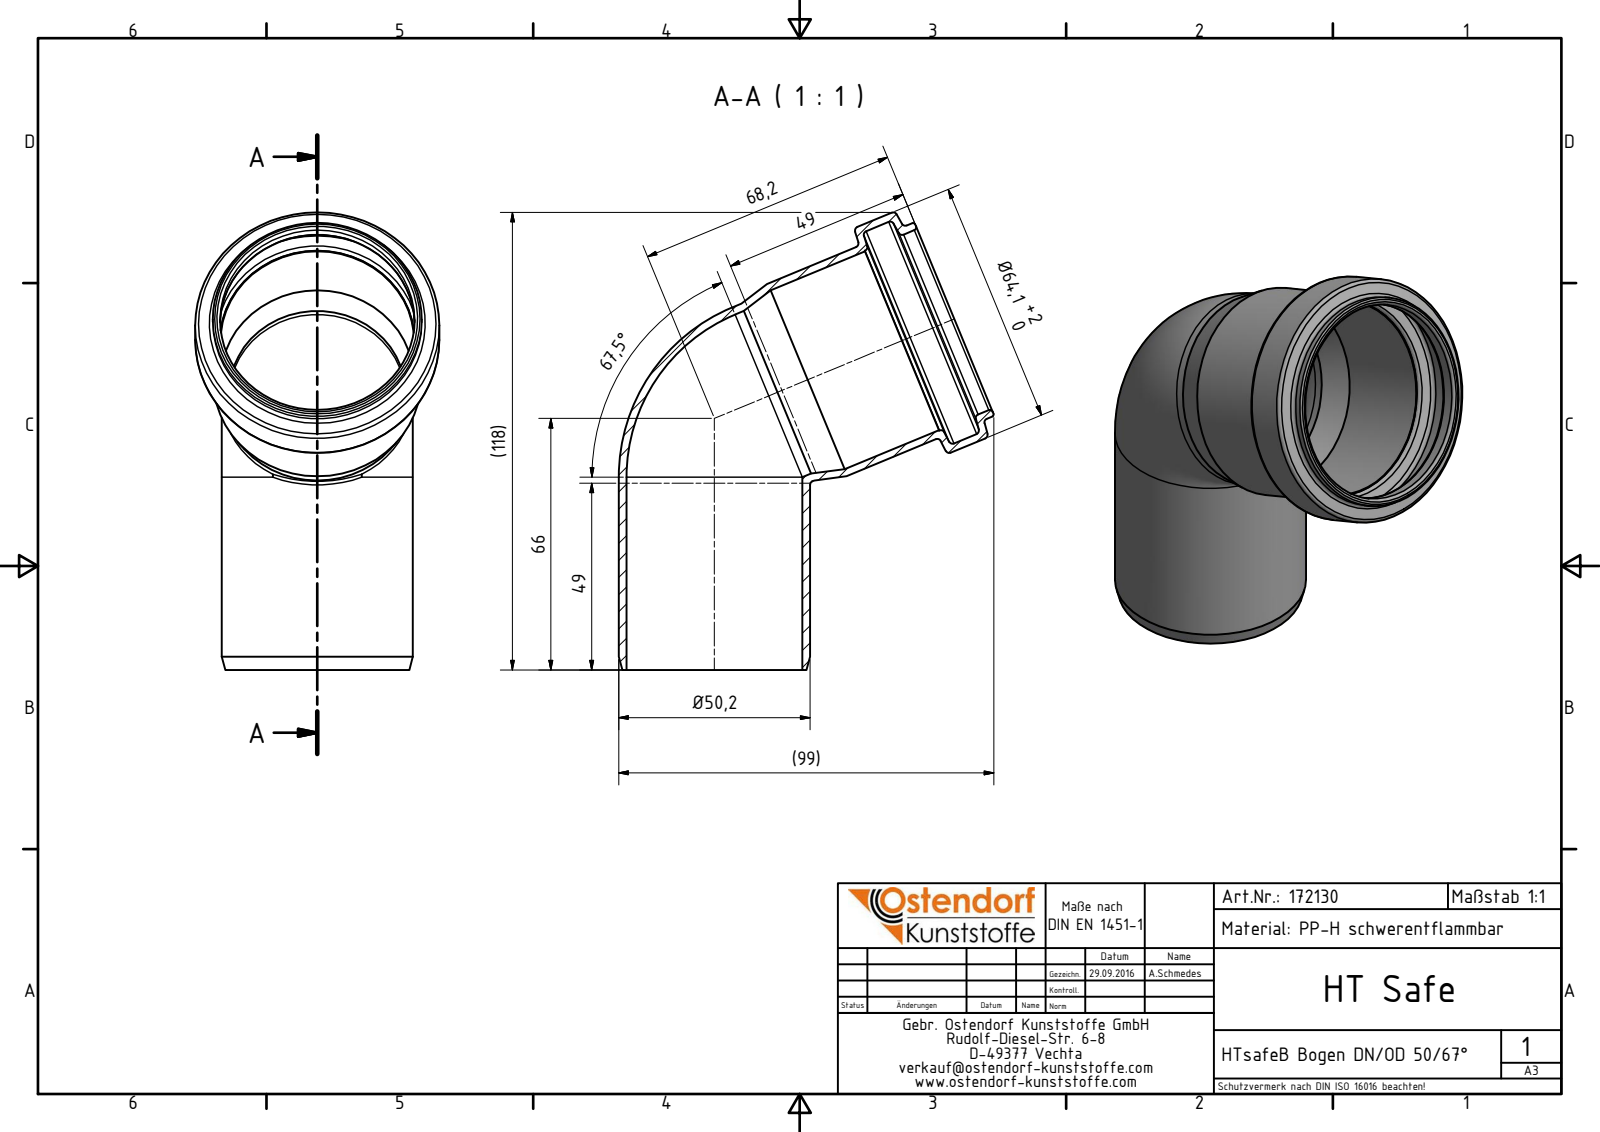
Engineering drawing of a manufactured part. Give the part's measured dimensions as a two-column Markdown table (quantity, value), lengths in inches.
| quantity | value |
| --- | --- |
| part name | 172130 HTsafeB DN_OD 50_67° |
| STEP written by | Autodesk Inventor 2016 (AUTOMOTIVE_DESIGN) |
| units | inches |
| bodies | 1 solid, 34 faces (3 planar, 11 cylindrical, 20 other) |
| overall size | 4.727 × 3.876 × 2.524 |
| volume | 2.512 in³ |
| surface area | 69.01 in² |
| round holes (diameter × count) | 1.819 × 2, 2.012 × 2, 2 × 1, 2.374 × 1 |
| round bosses / shafts (diameter × count) | 1.976 × 2, 2.524 × 1, 2.161 × 1, 2.15 × 1 |
| main face-to-face distances | 0.587 |
